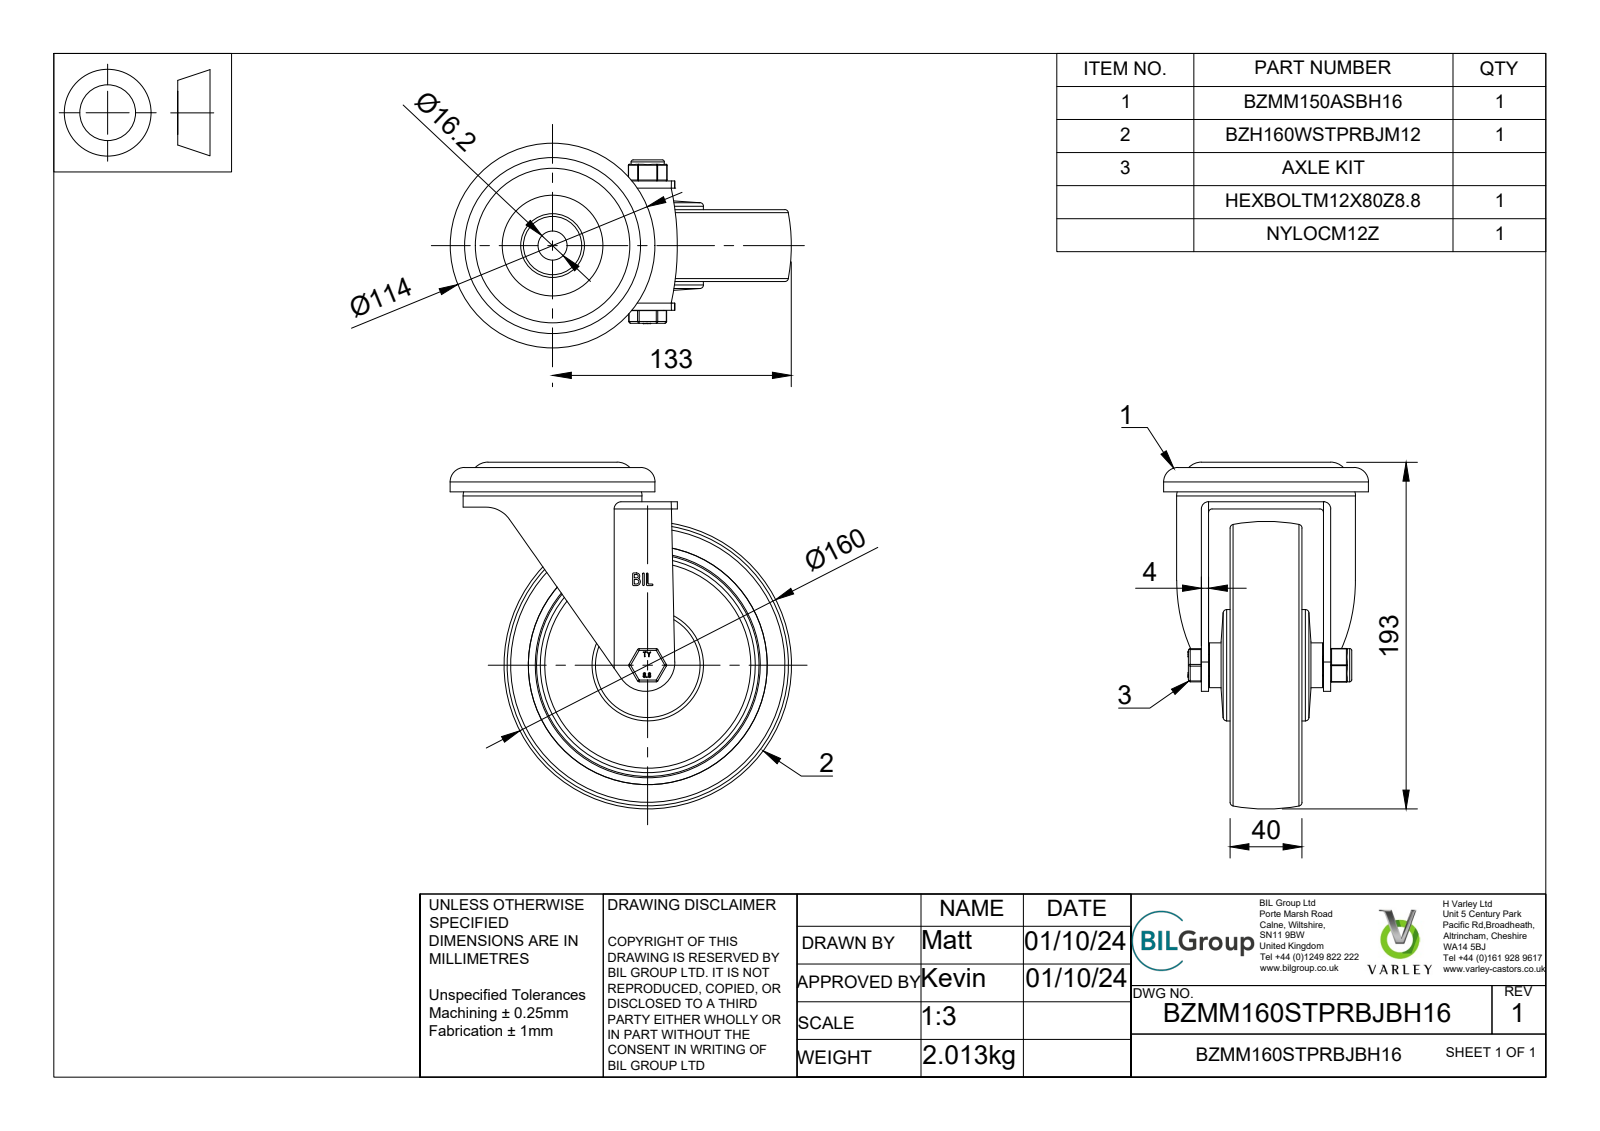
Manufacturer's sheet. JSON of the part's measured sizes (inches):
{"part_name": "BZMM160STPRBJBH16 v3; BZMM150ASBH16 - 64 v1; ZINC PLATED, PRESSED STEEL HEAD; ZINC PLATED, PRESSED STEEL FORKS (+7 more)", "step_written_by": "Autodesk Translation Framework v13.20.0.188 (AUTOMOTIVE_DESIGN)", "units": "inches", "bodies": {"solids": 22, "faces": 773, "planar": 319, "cylindrical": 165, "other": 289}, "overall_size": [7.598, 7.48, 4.488], "volume_in3": 40.34, "surface_area_in2": 382.5, "round_holes": [[0.472, 1], [0.48, 1], [0.496, 1], [0.551, 1], [0.638, 1], [0.787, 1], [1.122, 1], [1.213, 1], [1.587, 1], [1.594, 1], [1.614, 1], [1.654, 1]], "round_bosses_or_shafts": [[4.488, 1], [3.917, 1], [2.913, 1], [2.441, 1], [2.224, 1], [1.89, 1], [1.85, 1], [1.606, 1]], "partial_cylinders_radius": [[0.02, 18], [0.039, 12], [0.079, 4], [0.157, 2], [0.63, 1], [0.641, 1], [0.65, 1], [0.768, 1]], "face_to_face_distances": [0.915, 0.659, 0.256, 0.472, 1.132, 1.388, 2.047, 1.575, 0.157, 0.374]}
